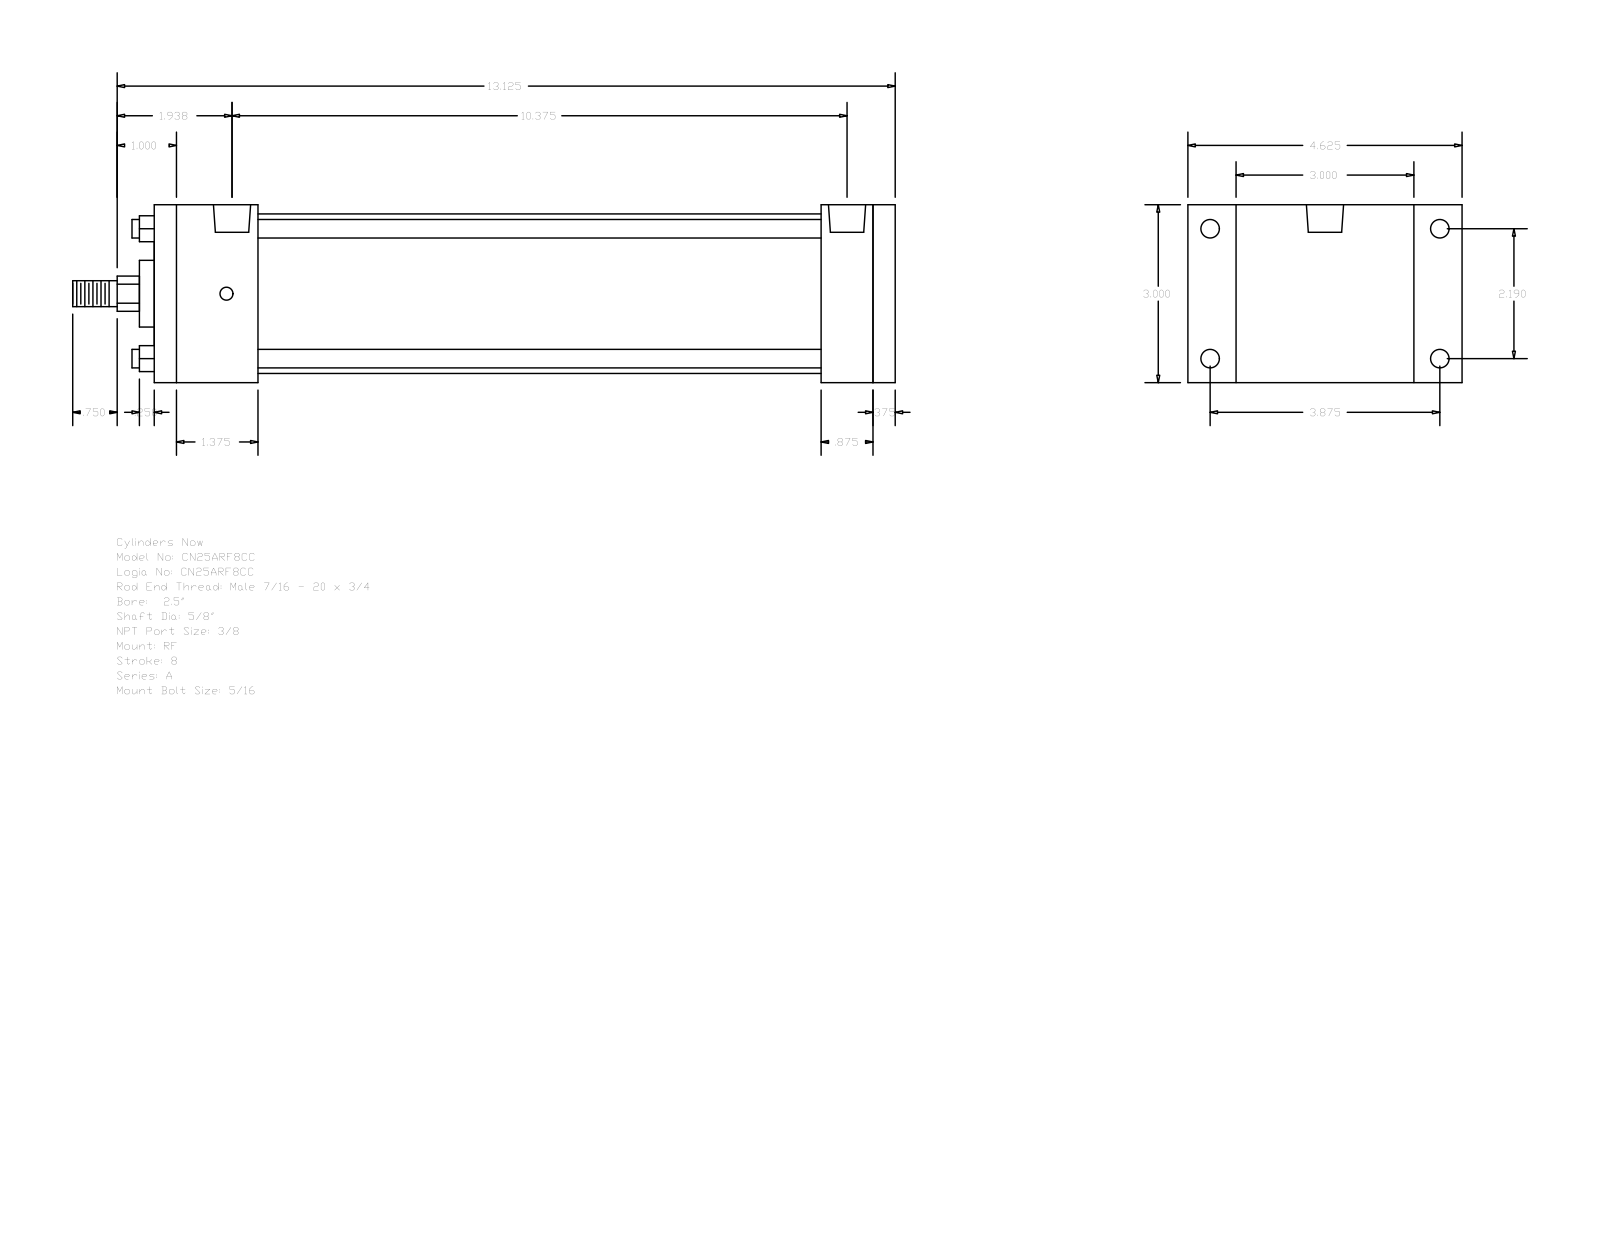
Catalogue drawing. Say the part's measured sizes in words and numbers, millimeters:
The part is named "A_RF__0250_0.625". Its 3-D file was written by "GSSL Pune (CONFIG_CONTROL_DESIGN)". It is 0 solids with 92 faces: 64 planar, 28 cylindrical and 0 other. Overall it measures 352.43 by 117.47 by 76.2 millimeters. Round holes: 4 of diameter 5.56, 4 of diameter 7.94, 2 of diameter 15.93. Round bosses or shafts: 4 of diameter 7.94, 1 of diameter 68.33, 1 of diameter 28.57, 1 of diameter 15.88, 1 of diameter 11.11. Partial cylindrical surfaces (rounded edges, fillets, slot ends): 1 of radius 7.54. The main face-to-face distances are 76.2, 317.5, 9.53, 307.97, 44.45, 285.74, 241.29, 263.52, 273.05, 22.23. The hole center spacings are 2.38, 55.62, 98.42, 113.05, 265.91, 268.29, 263.53.
